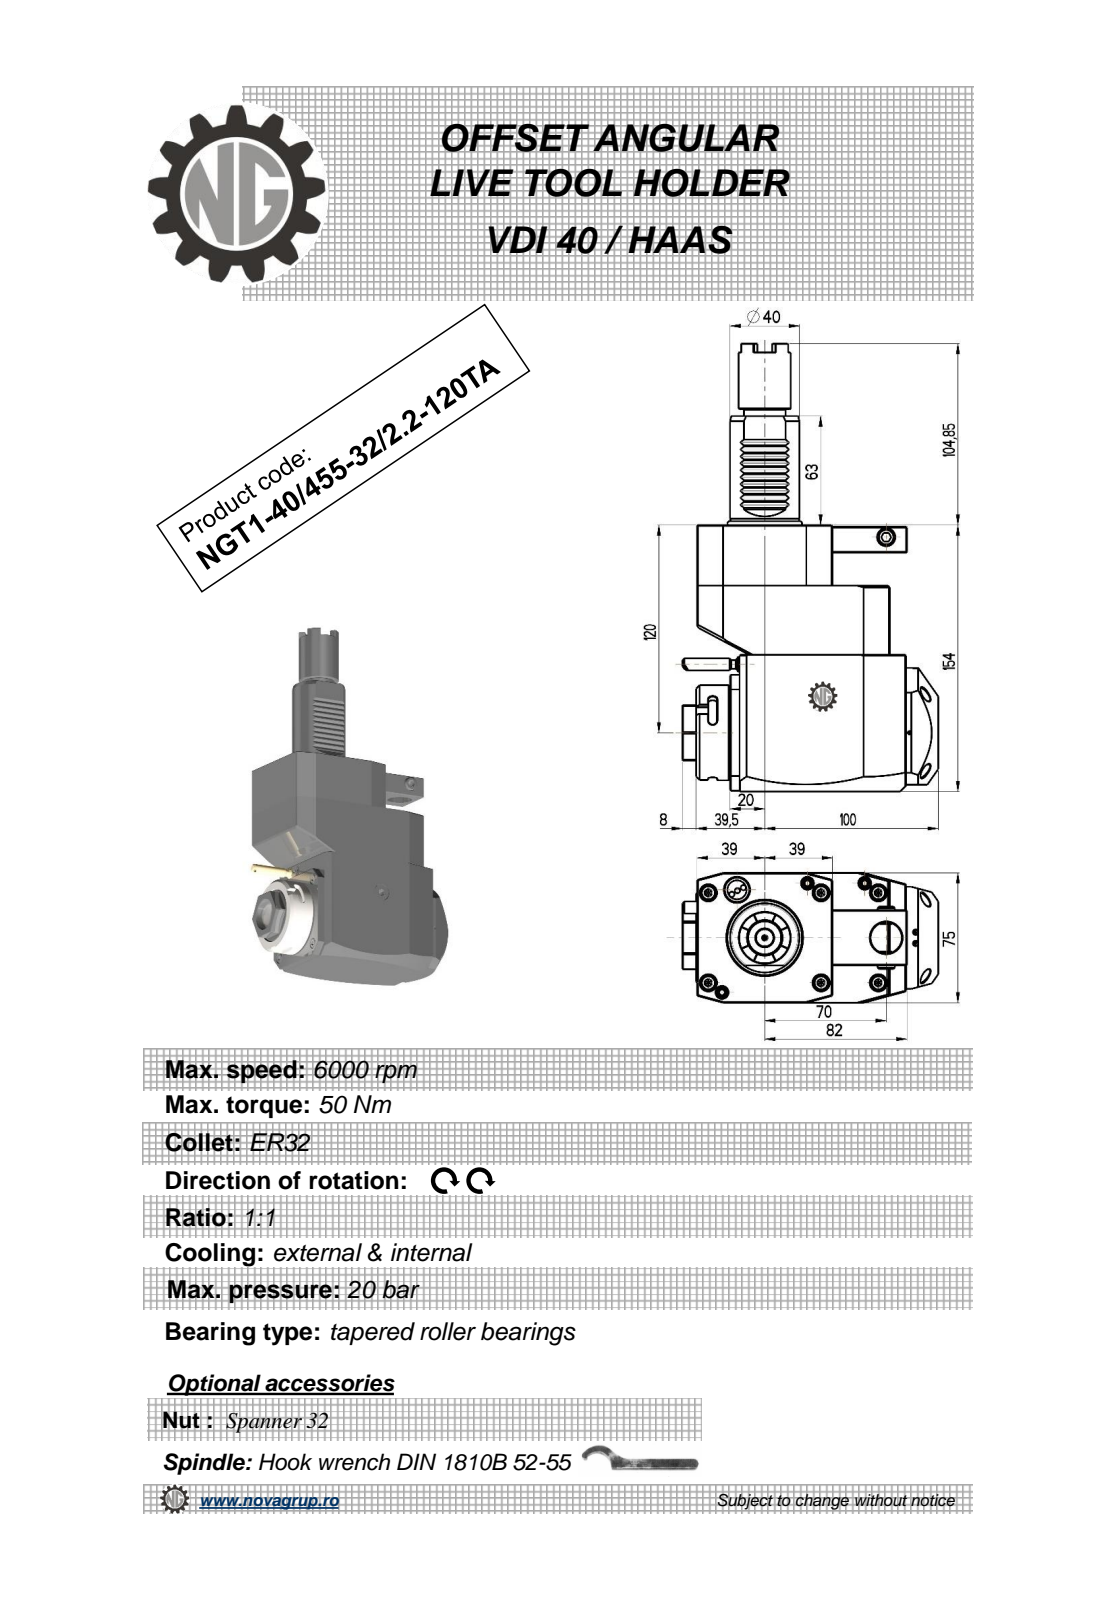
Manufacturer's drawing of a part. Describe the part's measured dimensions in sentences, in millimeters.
The part is named "NGT1_40_455_32_1_2_120TA". Its 3-D file was written by "PRO/ENGINEER BY PARAMETRIC TECHNOLOGY CORPORATION, 2010280 (CONFIG_CONTROL_DESIGN)". It is 1 solid with 374 faces: 222 planar, 70 cylindrical and 82 other. Overall it measures 258.85 by 147.5 by 75 millimeters. Its volume is 1 305 000 cubic millimeters and its surface area 95 167 square millimeters. Round holes: 1 of diameter 2.5, 1 of diameter 3, 1 of diameter 9.5, 1 of diameter 18, 1 of diameter 23. Round bosses or shafts: 2 of diameter 8.96, 1 of diameter 55, 1 of diameter 48, 1 of diameter 40, 1 of diameter 30, 1 of diameter 20, 1 of diameter 10, 1 of diameter 7. Partial cylindrical surfaces (rounded edges, fillets, slot ends): 10 of radius 0.3, 6 of radius 2.5, 2 of radius 180, 1 of radius 0.5, 1 of radius 4.25, 1 of radius 24.5, 1 of radius 37.5. The main face-to-face distances are 75, 154, 19, 59, 0.5, 111, 33, 92, 35, 119. The hole center spacings are 43.2, 75.07, 112.5.
